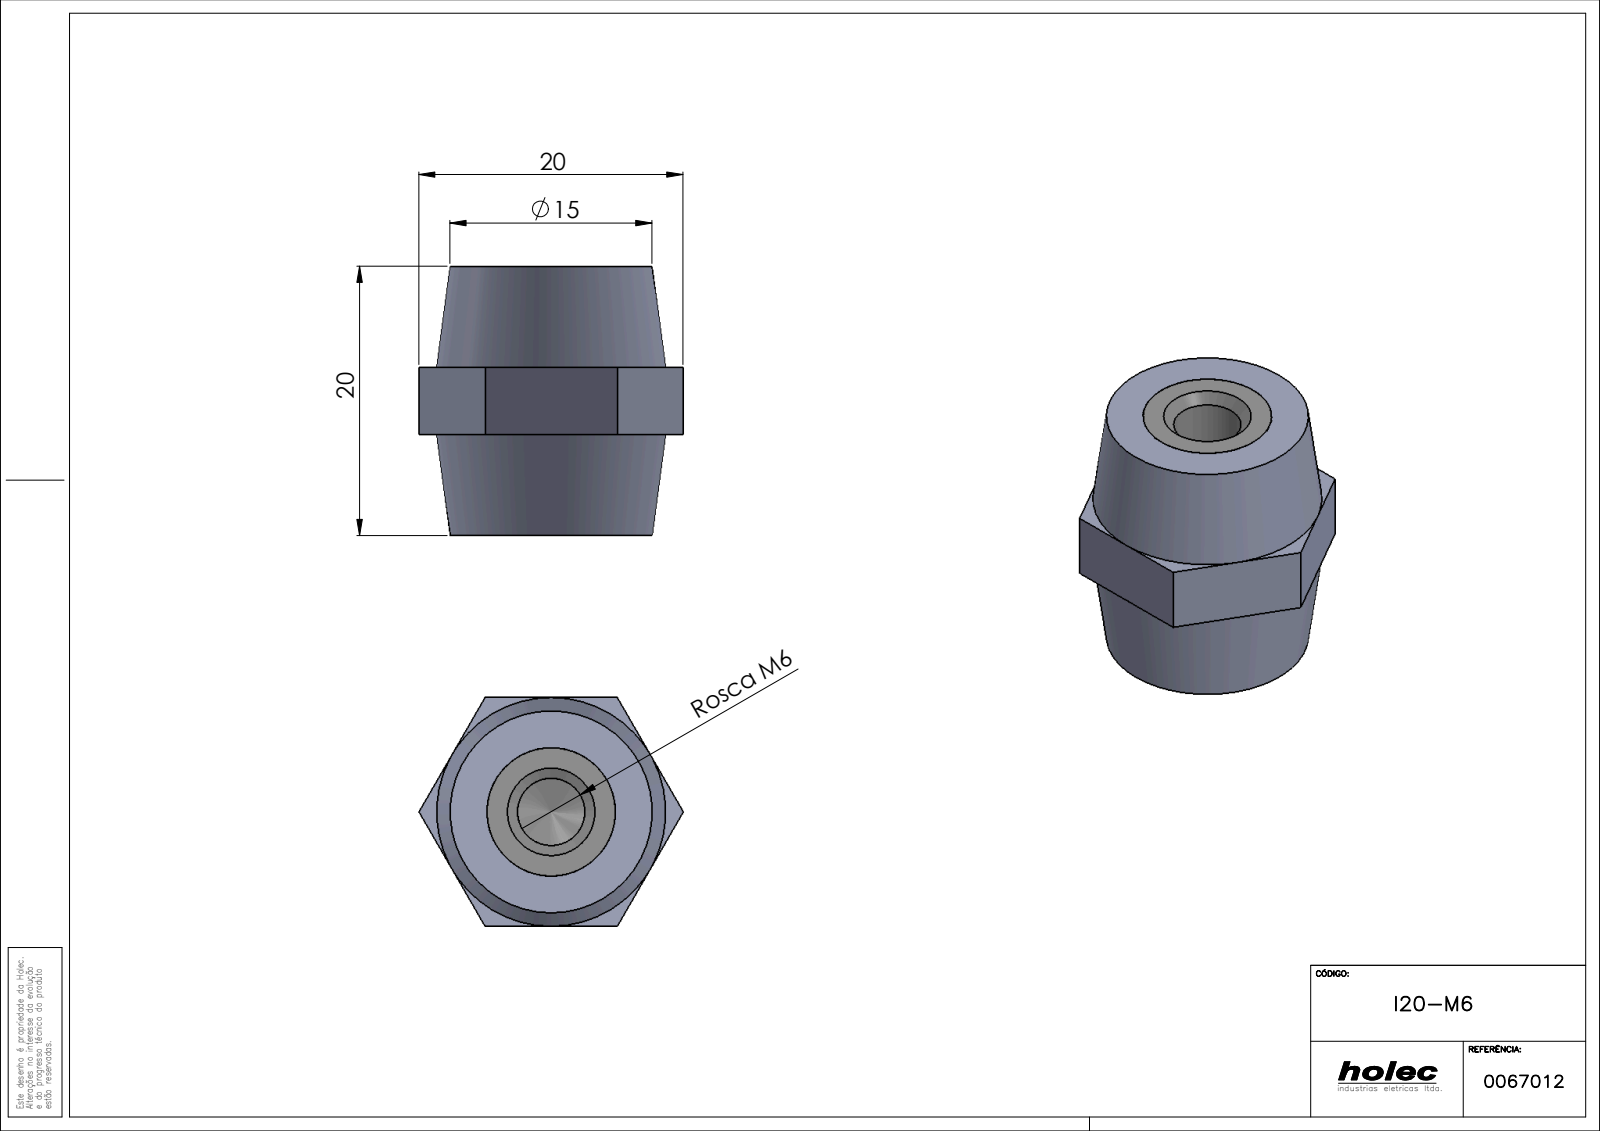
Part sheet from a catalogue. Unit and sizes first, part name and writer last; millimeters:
Units: millimetres
Overall size (bounding box): 20 × 19.63 × 17
Round holes (diameter × count): ⌀5 ×1, ⌀8 ×1
Main face-to-face distances: 3.74, 13.26, 9.52, 6.5, 17, 20, 6.49, 13.51, 13.5, 7.01
Volume: 4 067 mm³ · Surface area: 2 880 mm²
Bodies: 3 solids, 162 faces (82 planar, 12 cylindrical, 68 other)
Part name (STEP PRODUCT): PB1_0100(PB1_0100_06); PB1_0007; I20-M6
STEP written by: SolidWorks 2017 (AUTOMOTIVE_DESIGN)
